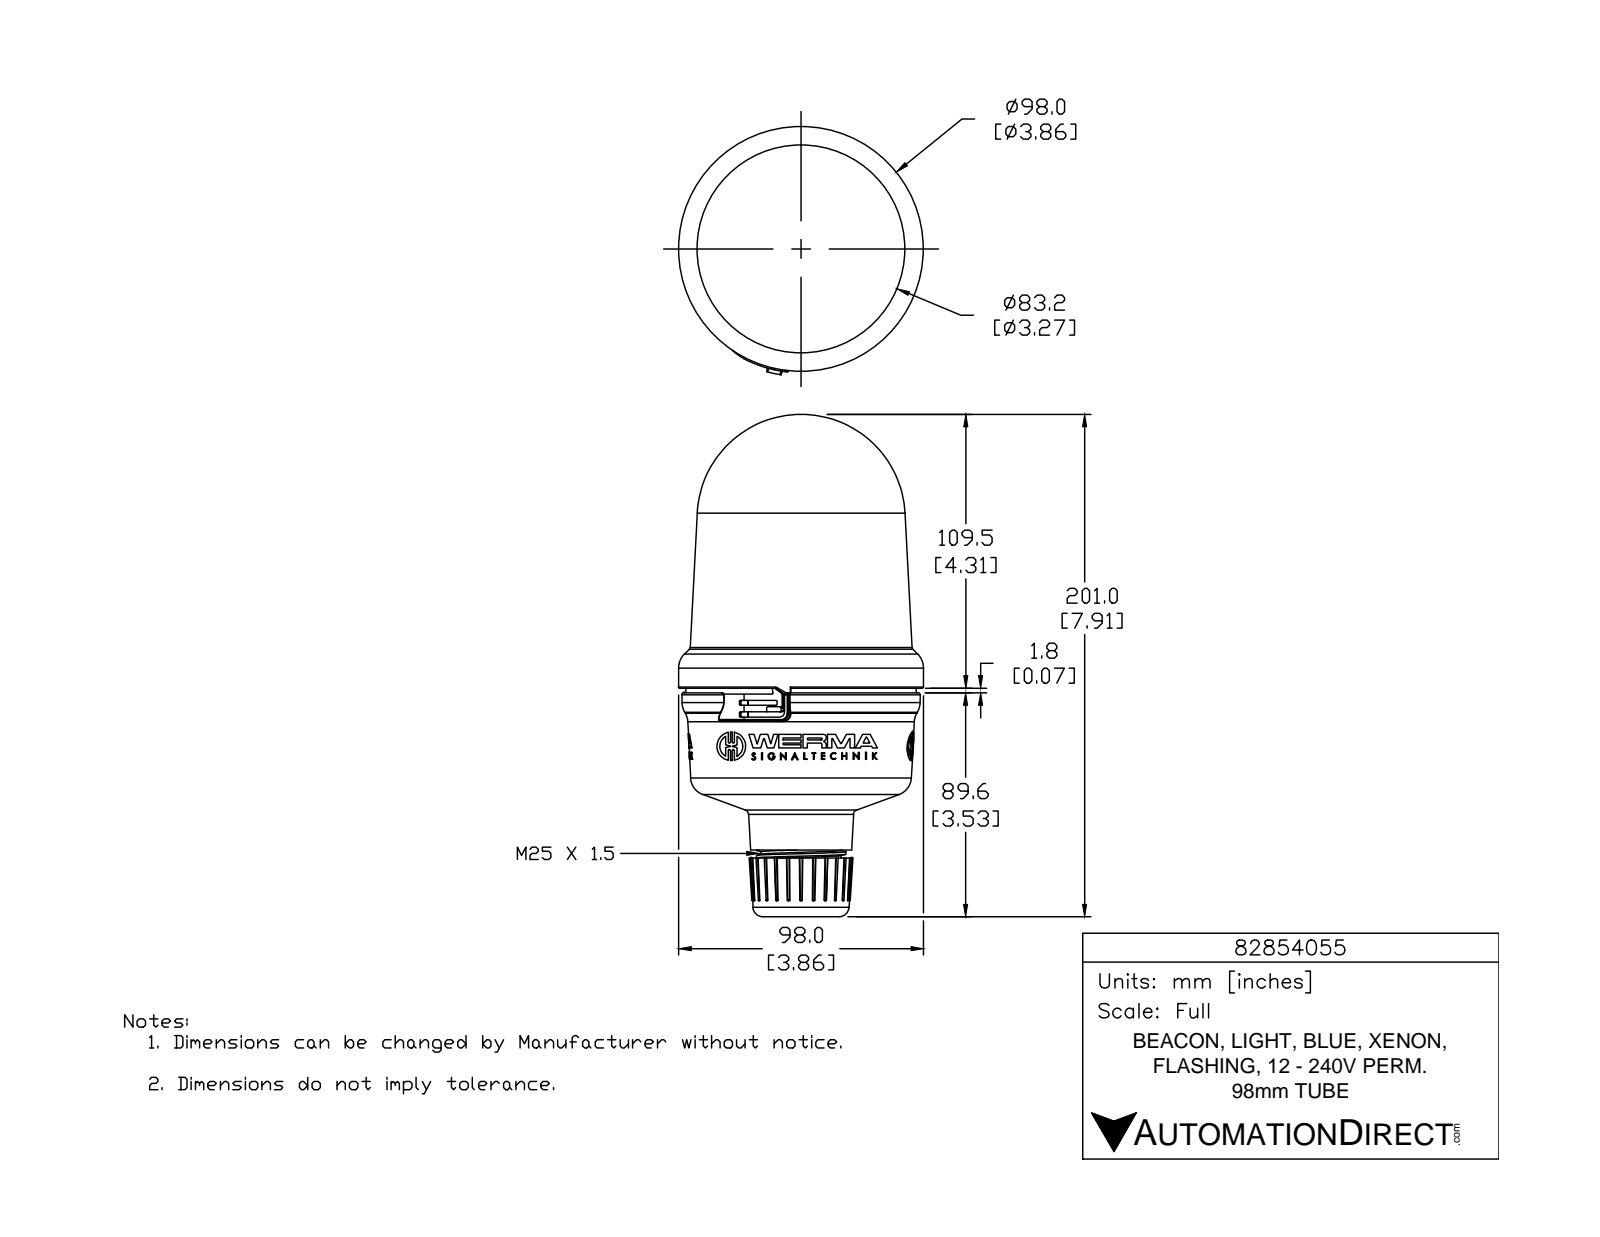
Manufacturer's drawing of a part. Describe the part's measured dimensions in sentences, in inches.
The part is named "82854055". Its 3-D file was written by "SolidWorks 2015 (AUTOMOTIVE_DESIGN)". It is 1 solid with 1006 faces: 554 planar, 189 cylindrical and 263 other. Overall it measures 7.914 by 3.912 by 3.858 inches. Its volume is 54.7 cubic inches and its surface area 91.39 square inches. Round holes: 3 of diameter 0.078, 1 of diameter 1.013, 1 of diameter 1.024. Round bosses or shafts: 3 of diameter 0.452, 3 of diameter 0.113, 1 of diameter 3.858, 1 of diameter 1.409, 1 of diameter 1.261. Partial cylindrical surfaces (rounded edges, fillets, slot ends): 12 of radius 0.02, 9 of radius 0.007, 6 of radius 0.007, 6 of radius 0.016, 6 of radius 0.016, 6 of radius 0.016, 6 of radius 0.262, 3 of radius 0.006. The main face-to-face distances are 2.214, 0.462, 2.676, 0.335, 0.127, 2.548, 2.603, 2.476, 2.141, 0.073.
